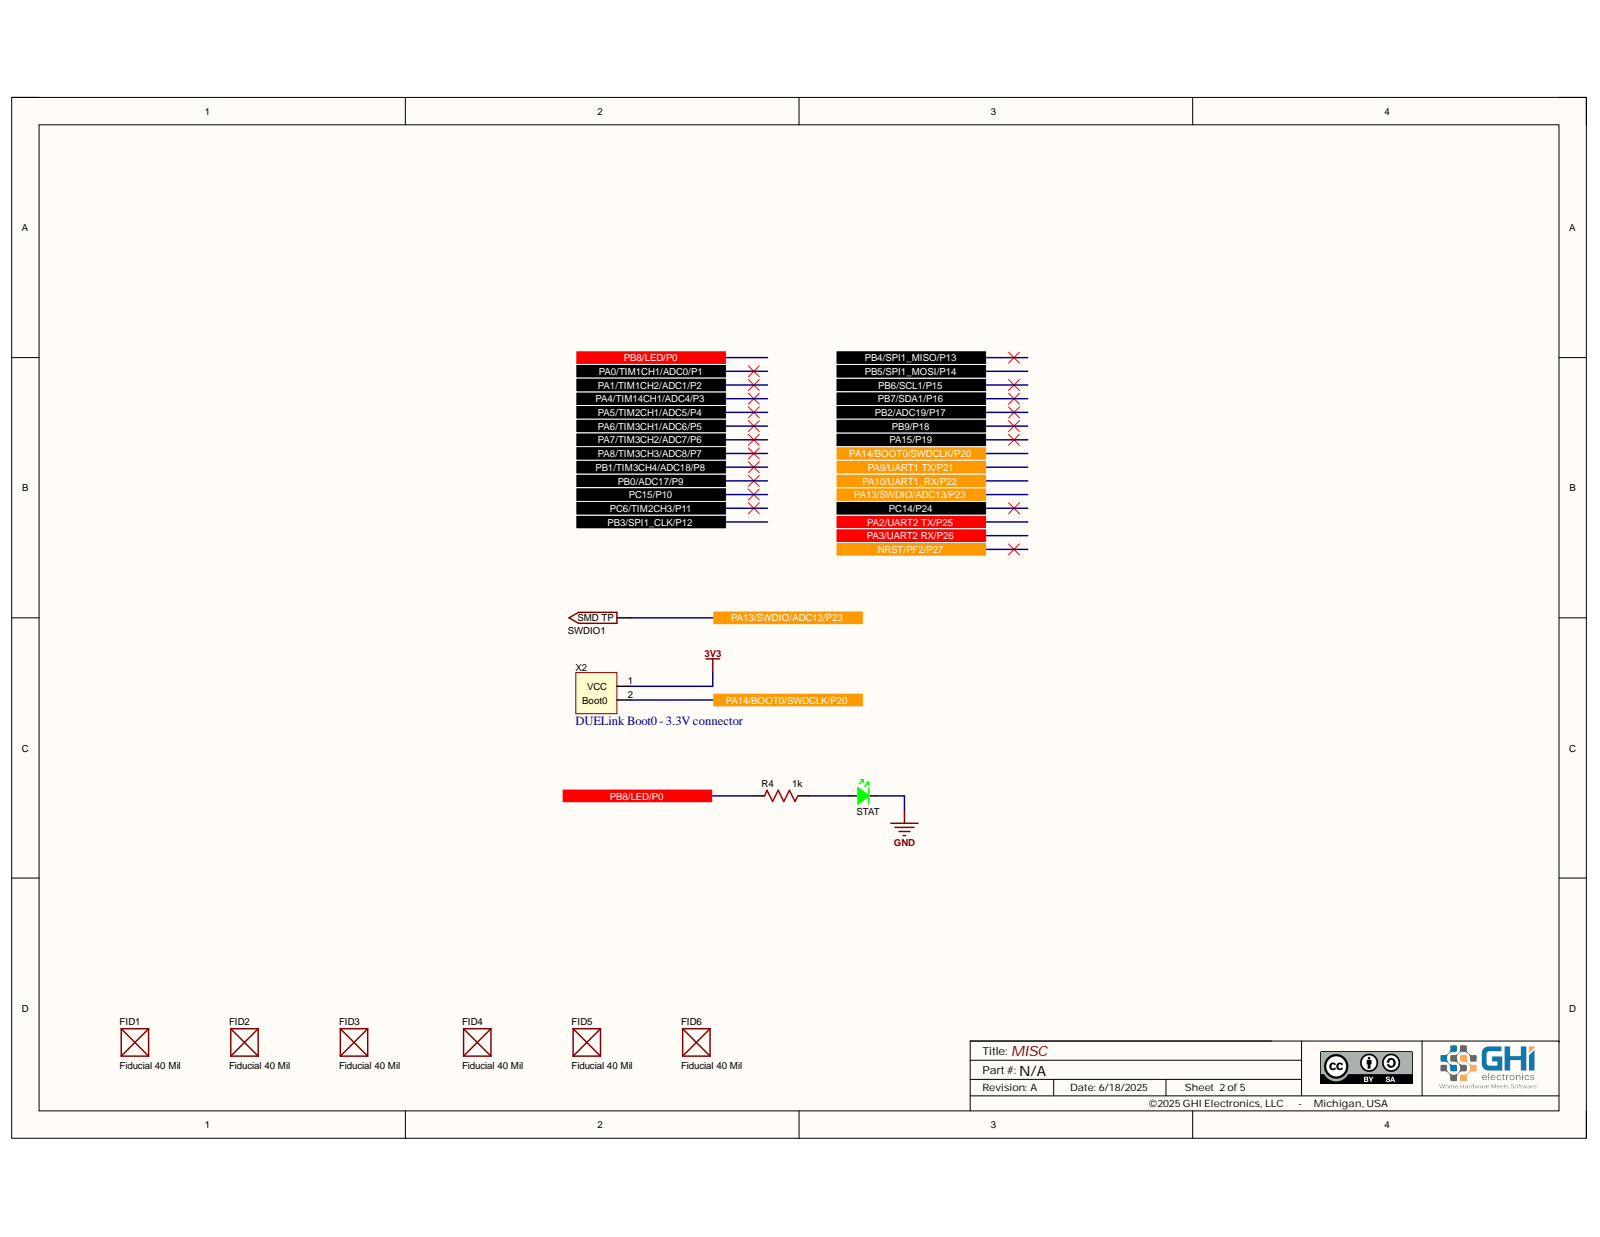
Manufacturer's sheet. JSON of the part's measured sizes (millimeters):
{"part_name": "PCB; Board; U; DUELink-U-Connector-BM04B-SRSS-TB (+7 more)", "step_written_by": "Open CASCADE 7.5 (AUTOMOTIVE_DESIGN)", "units": "millimeters", "bodies": {"solids": 89, "faces": 1556, "planar": 1161, "cylindrical": 274, "other": 121}, "overall_size": [27, 22, 13.4], "volume_mm3": 1793, "surface_area_mm2": 3858, "round_holes": [[3, 5], [0.6, 3], [1.3, 3], [2, 3], [2.75, 3], [3.5, 3], [1.02, 2]], "round_bosses_or_shafts": [[2.5, 3], [1, 3]], "partial_cylinders_radius": [[0.12, 35], [0.15, 14], [0.8, 12], [0.2, 6], [0.47, 3], [0.1, 2], [0.17, 2], [0.18, 2]], "face_to_face_distances": [1.6, 5, 4, 5.5, 10.5, 9.5, 0.5, 6, 9, 14.5], "hole_center_spacings": [5, 5.94, 3.2, 10, 10.5, 12.08, 14.87, 15.05]}
